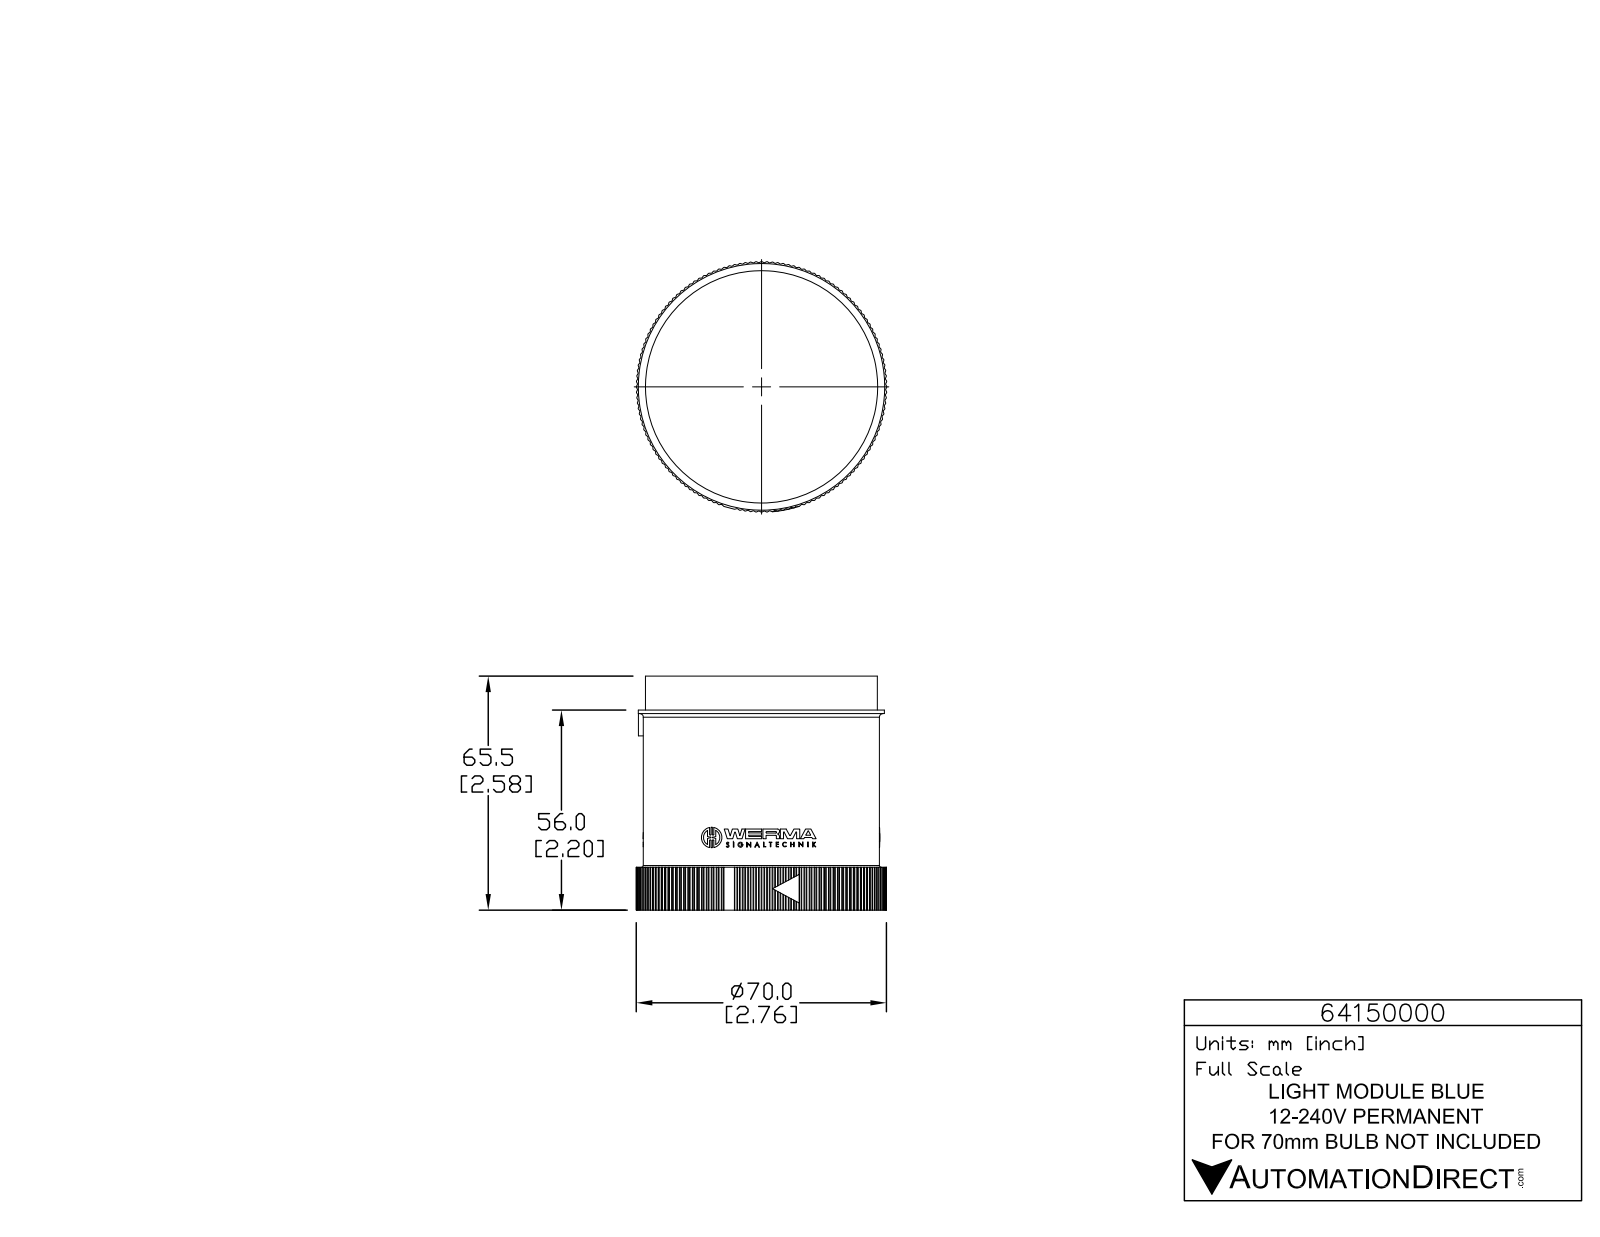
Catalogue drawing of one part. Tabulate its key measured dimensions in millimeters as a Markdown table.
| quantity | value |
| --- | --- |
| part name | 64150000 |
| STEP written by | SolidWorks 2015 (AUTOMOTIVE_DESIGN) |
| units | millimeters |
| bodies | 1 solid, 1400 faces (832 planar, 563 cylindrical, 5 other) |
| overall size | 70.2 × 70.2 × 65.5 |
| volume | 197 000 mm³ |
| surface area | 24 180 mm² |
| round holes (diameter × count) | 1 × 3, 65.4 × 1 |
| round bosses / shafts (diameter × count) | 5.7 × 3, 1.4 × 3, 69 × 1, 66.2 × 1, 65 × 1 |
| partial cylindrical surfaces (radius × count) | 0.2 × 285, 0.2 × 6, 0.2 × 6, 0.2 × 6, 3.3 × 6, 0.1 × 3, 0.1 × 3, 0.2 × 3 |
| main face-to-face distances | 55.9, 62.3, 9.6, 65.5, 56, 46.4, 9.5, 62.3, 12, 2.4 |
